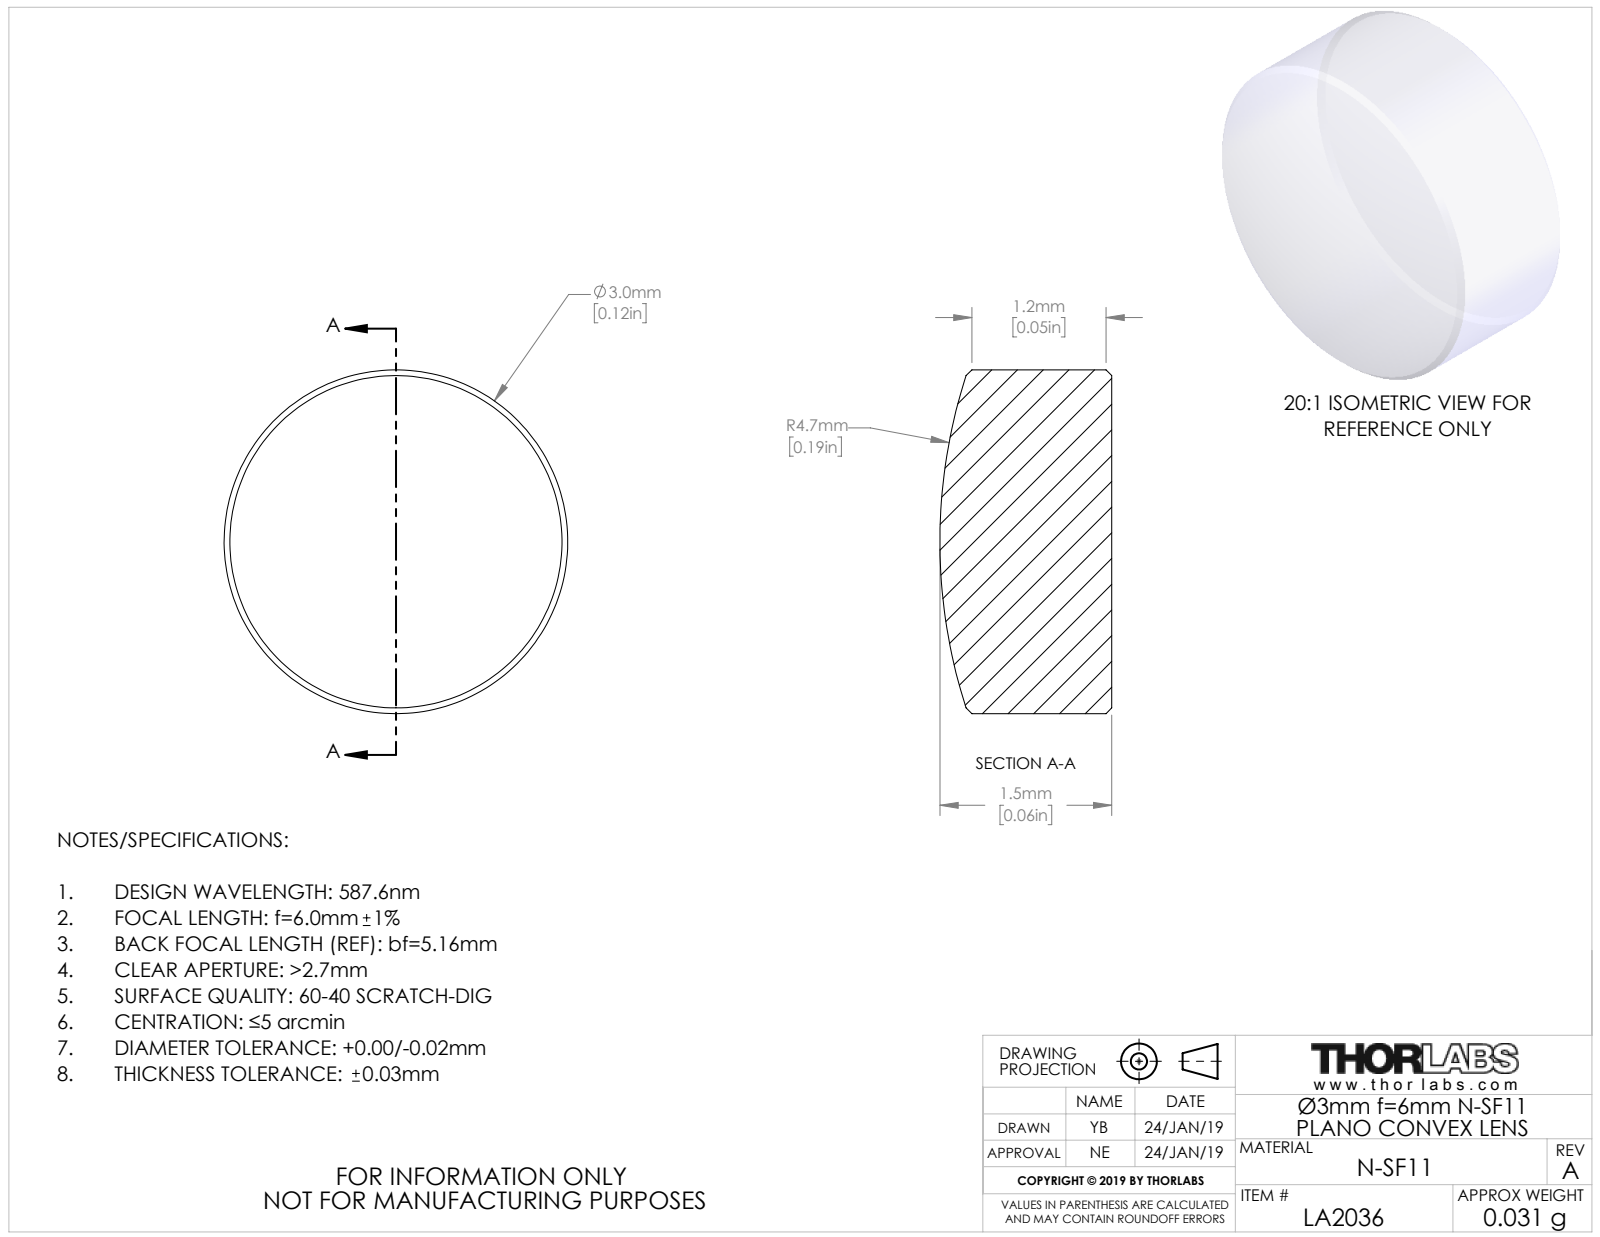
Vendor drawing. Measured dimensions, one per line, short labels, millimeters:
name: TTN162743-E0W
written by: SolidWorks 2018 (CONFIG_CONTROL_DESIGN)
unit: mm
bodies: 1 solid, 9 faces (1 planar, 2 cylindrical, 6 other)
size: 3 × 3 × 1.5
volume: 10 mm³; area: 26 mm²
bosses: 1× ⌀3
